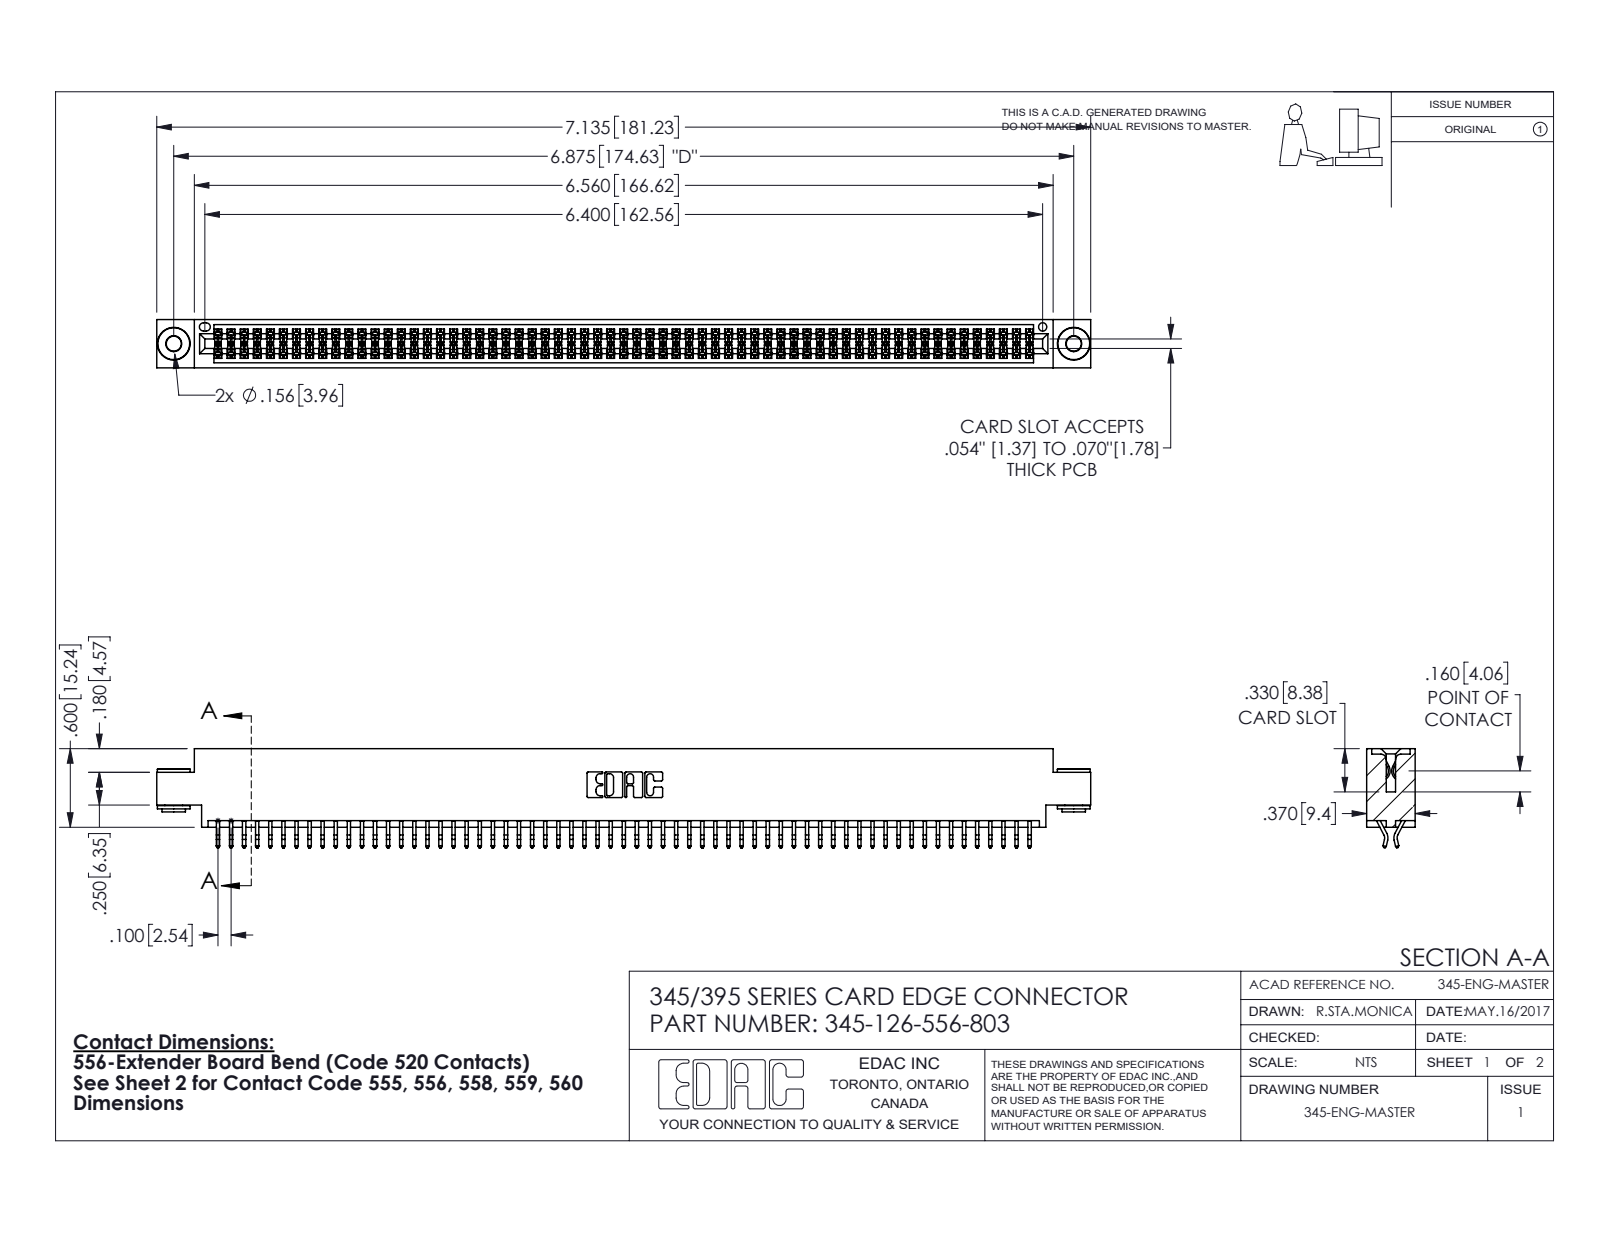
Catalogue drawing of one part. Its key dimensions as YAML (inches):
part_name: "345-126-556-803; 345-250-002_345-250-002-102; 345-292-001_556 Tail; 345 Part_0.170 Offset - 0.156 Dia-TH"
step_written_by: "SolidWorks 2016 (CONFIG_CONTROL_DESIGN)"
units: inches
bodies: {solids: 129, faces: 7224, planar: 4756, cylindrical: 2460, other: 8}
overall_size: [7.135, 0.757, 0.37]
volume: 1.08
surface_area: 41.55
round_holes:
  - {diameter: 0.116, count: 2}
  - {diameter: 0.156, count: 2}
  - {diameter: 0.064, count: 1}
round_bosses_or_shafts:
  - {diameter: 0.25, count: 2}
  - {diameter: 0.18, count: 2}
  - {diameter: 0.136, count: 2}
partial_cylinders:
  - {radius: 0.006, count: 189}
  - {radius: 0.01, count: 22}
  - {radius: 0.007, count: 6}
  - {radius: 0.031, count: 6}
  - {radius: 0.026, count: 3}
  - {radius: 0.01, count: 2}
  - {radius: 0.014, count: 2}
  - {radius: 0.019, count: 2}
face_to_face_distances: [0.072, 0.298, 0.37, 0.2, 0.025, 0.098, 0.272, 0.225, 0.175, 0.149]
hole_center_spacings: [0.27, 6.639, 6.875]
